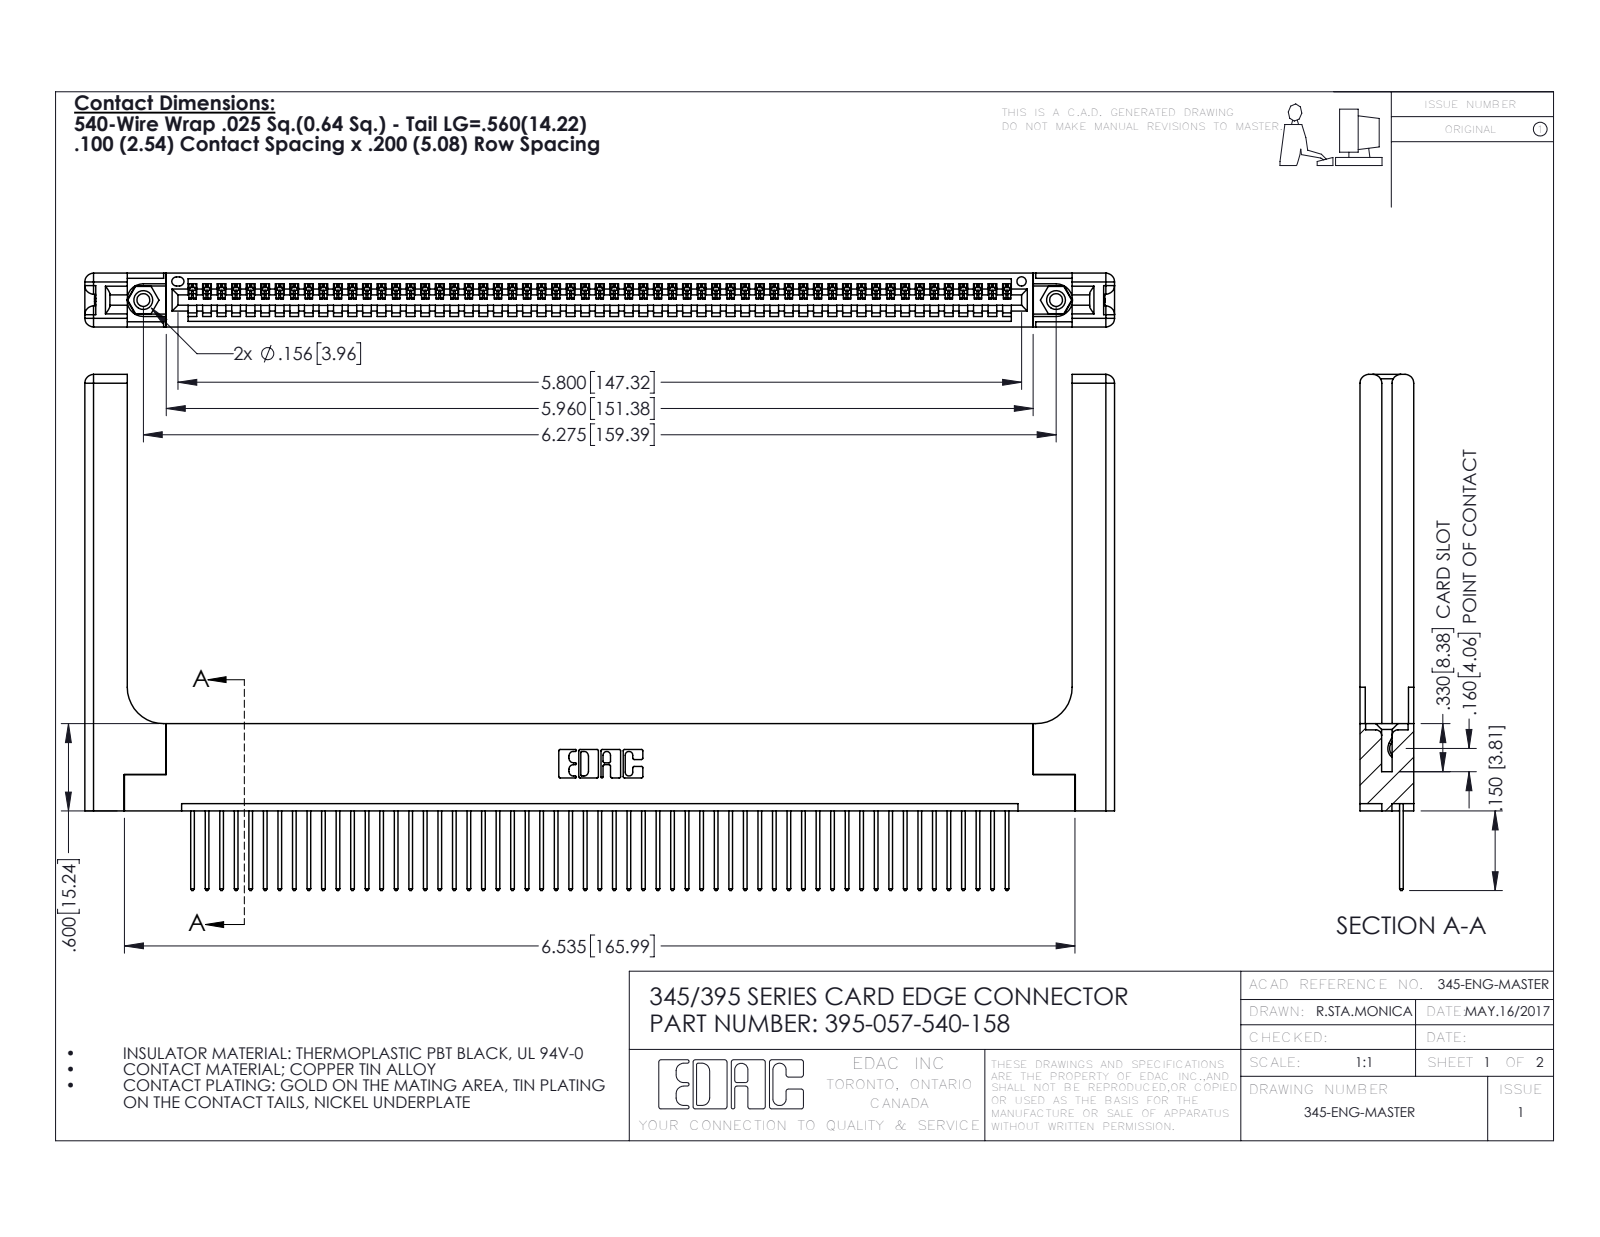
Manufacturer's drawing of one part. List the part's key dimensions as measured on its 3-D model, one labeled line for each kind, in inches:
Part name (STEP PRODUCT): 345-292-001_345-293-140; 345 Part_Flush Mounting Lugs - 0.156 Dia-TH; 345-250-001_345-250-001-102; 395-057-540-158 (+1 more)
STEP written by: SolidWorks 2016 (CONFIG_CONTROL_DESIGN)
Units: inches
Bodies: 62 solids, 3688 faces (2508 planar, 1120 cylindrical, 60 other)
Overall size (bounding box): 7.079 × 3.547 × 0.37
Volume: 1.573 in³ · Surface area: 44.99 in²
Round holes (diameter × count): ⌀0.089 ×2, ⌀0.125 ×2, ⌀0.156 ×2, ⌀0.064 ×1
Round bosses / shafts (diameter × count): ⌀0.155 ×2
Partial cylindrical surfaces — rounded edges, fillets, slot ends (radius × count): R0.006 ×114, R0.01 ×114, R0.01 ×22, R0.06 ×16, R0.007 ×6, R0.031 ×6, R0.026 ×3, R0.03 ×2
Main face-to-face distances: 0.072, 0.298, 0.37, 0.098, 0.272, 0.025, 0.2, 0.225, 0.148, 0.15
Hole centre spacings: 0.27, 6.039, 6.275
